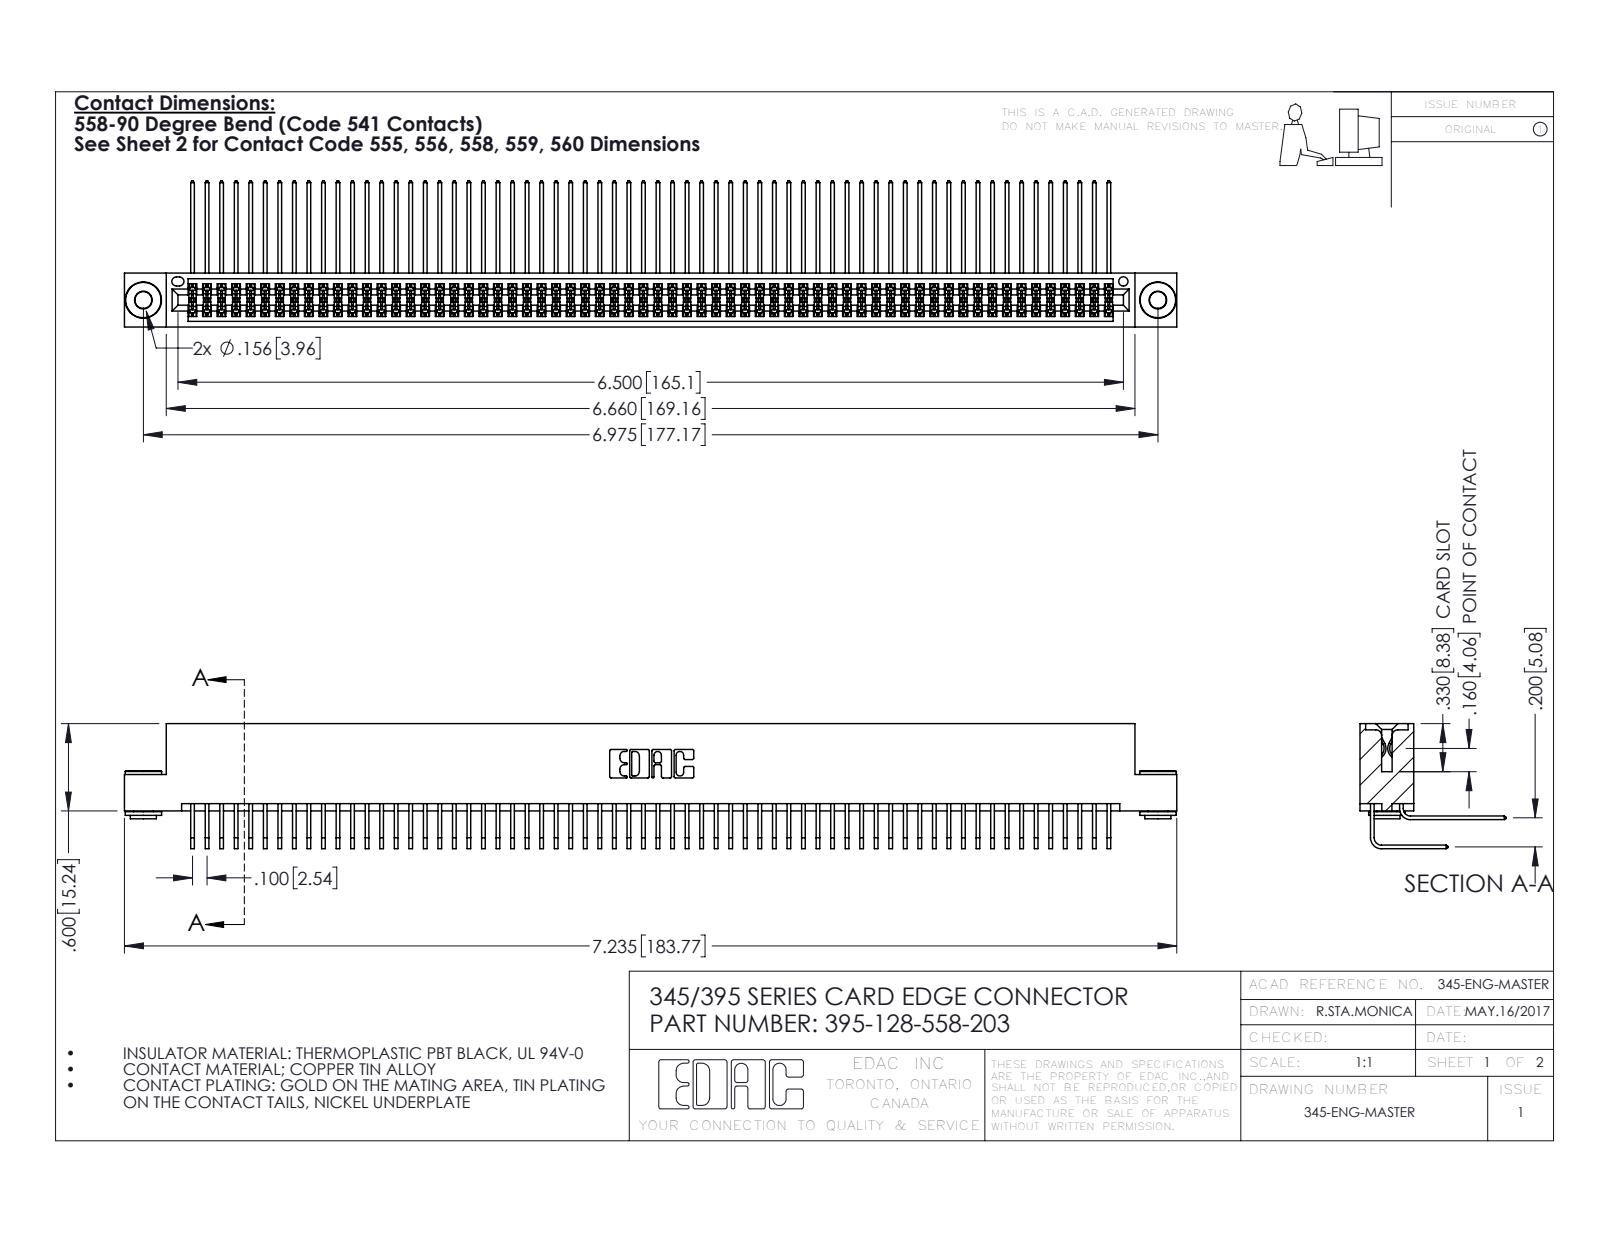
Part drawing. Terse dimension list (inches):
name: 345-250-002_345-250-002-102; 345-292-001_558 559 Tail - 1; 345-292-001_558 Tail - 2; 345 Part_Flush Mounting Lugs - 0.156 Dia-TH (+1 more)
written by: SolidWorks 2016 (CONFIG_CONTROL_DESIGN)
unit: in
bodies: 131 solids, 6820 faces (4570 planar, 2242 cylindrical, 8 other)
size: 7.235 × 1.005 × 0.859
volume: 1.148 in³; area: 49.46 in²
holes: 2× ⌀0.116, 2× ⌀0.156, 1× ⌀0.064
bosses: 2× ⌀0.25, 2× ⌀0.18, 2× ⌀0.136
rounds: 193× R0.006, 22× R0.01, 6× R0.007, 6× R0.031, 3× R0.026, 2× R0.014, 2× R0.019, 2× R0.022
face distances: 0.072, 0.298, 0.2, 0.37, 0.025, 0.098, 0.272, 0.225, 0.025, 0.175
hole spacings: 0.27, 6.739, 6.975
